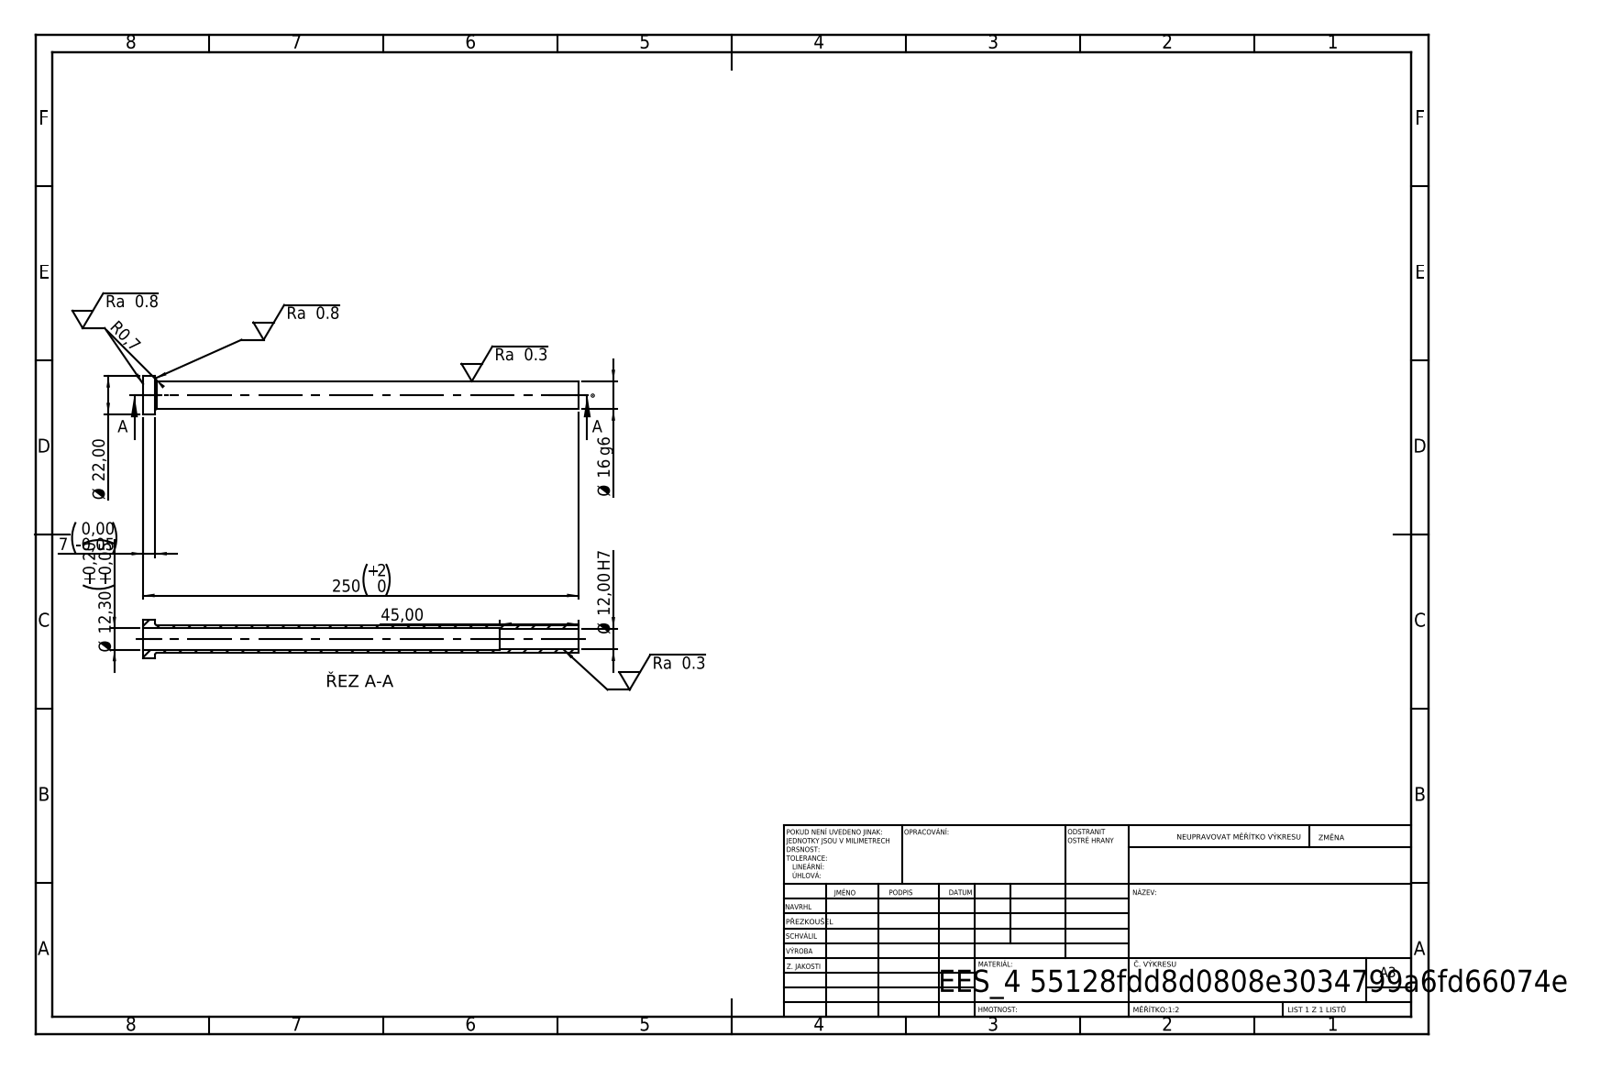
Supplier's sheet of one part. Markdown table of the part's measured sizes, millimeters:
| quantity | value |
| --- | --- |
| STEP written by | SolidWorks 2019 (CONFIG_CONTROL_DESIGN) |
| units | millimeters |
| bodies | 1 solid, 14 faces (4 planar, 8 cylindrical, 2 other) |
| overall size | 250 × 22 × 22 |
| volume | 22 076 mm³ |
| surface area | 22 835 mm² |
| round holes (diameter × count) | 12 × 1, 12.3 × 1 |
| round bosses / shafts (diameter × count) | 22 × 1, 16 × 1 |
| main face-to-face distances | 7, 250, 243, 205, 198, 45 |
